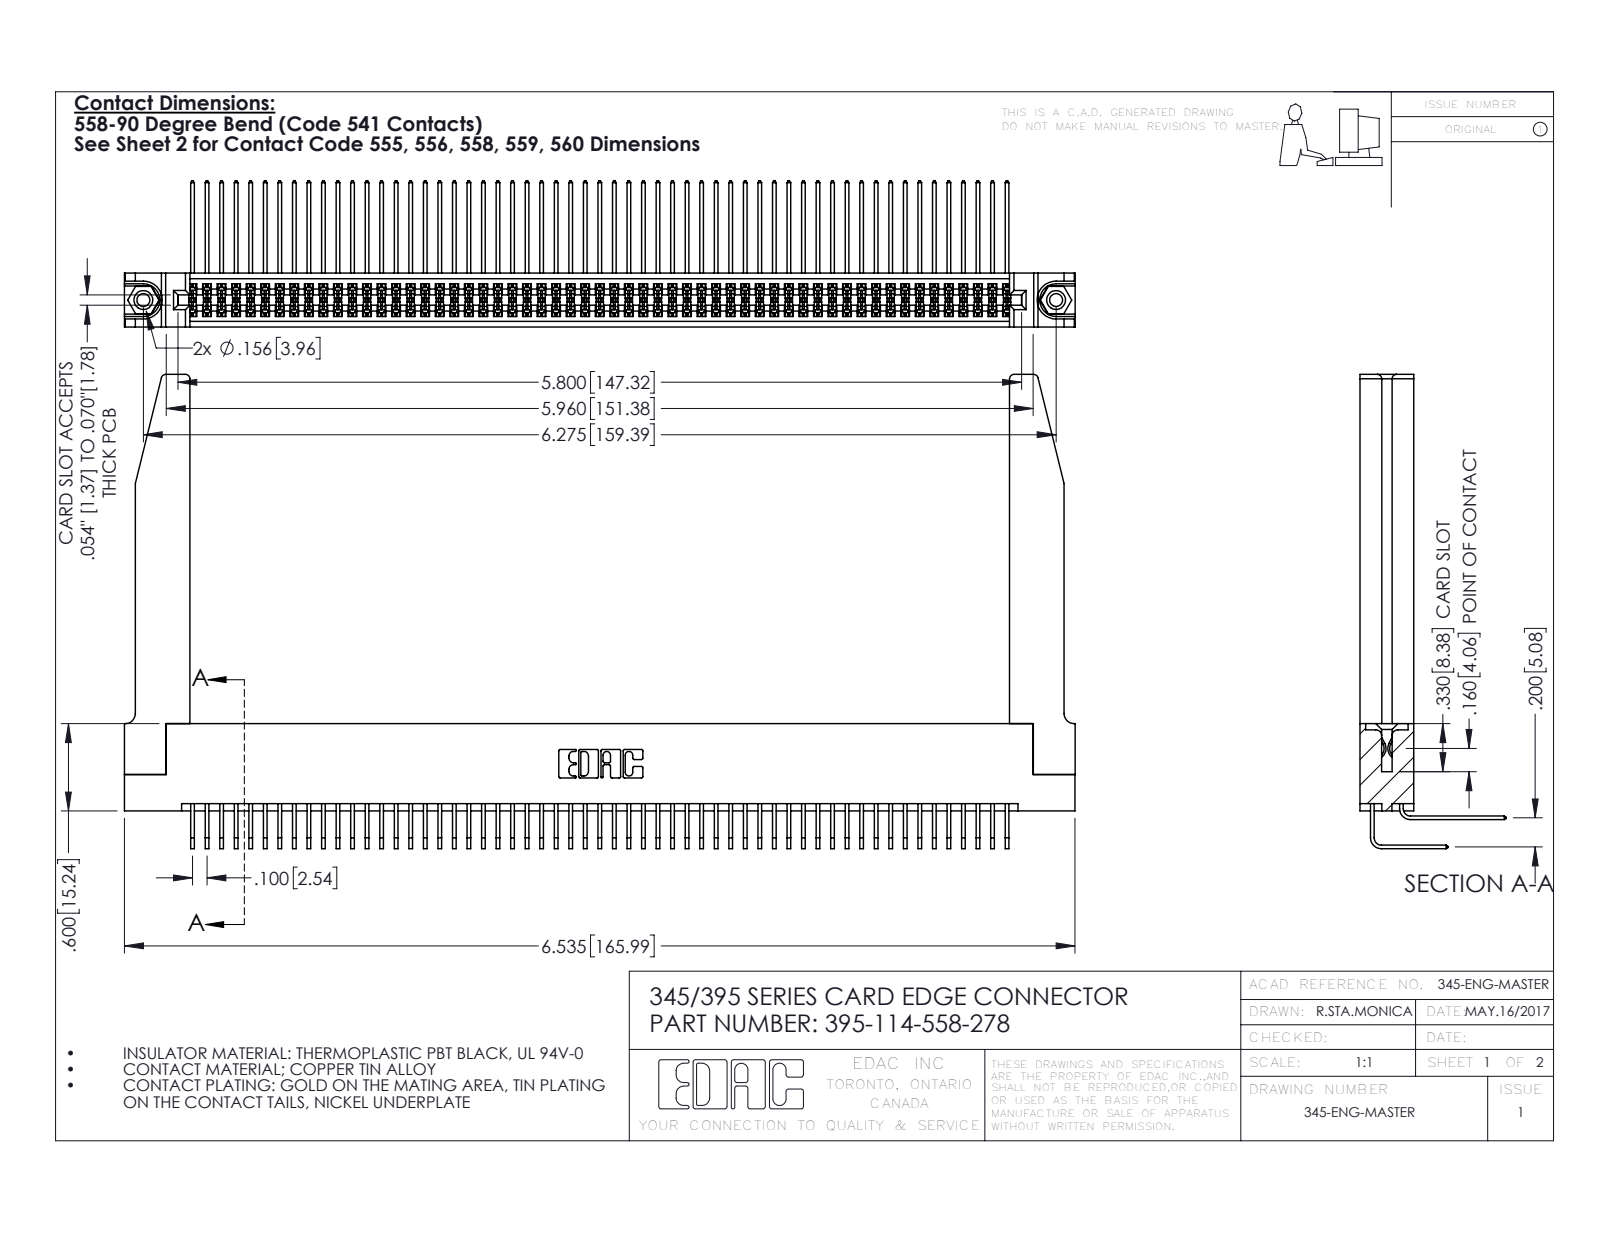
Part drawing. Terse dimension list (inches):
name: 345 Part_Flush Mounting Lugs - 0.156 Dia-TH; 345-292-001_558 Tail - 2; 345-220-078_345-220-078; 395-114-558-278 (+2 more)
written by: SolidWorks 2016 (CONFIG_CONTROL_DESIGN)
unit: in
bodies: 119 solids, 6288 faces (4212 planar, 2024 cylindrical, 52 other)
size: 6.536 × 3.259 × 1.005
volume: 1.507 in³; area: 54.62 in²
holes: 2× ⌀0.089, 2× ⌀0.125, 2× ⌀0.156, 1× ⌀0.064
bosses: 2× ⌀0.155
rounds: 172× R0.006, 22× R0.01, 8× R0.03, 6× R0.007, 6× R0.031, 3× R0.026, 2× R0.014, 2× R0.019
face distances: 0.072, 0.298, 0.37, 0.2, 0.098, 0.272, 0.025, 0.225, 0.025, 0.285
hole spacings: 0.27, 6.039, 6.275
